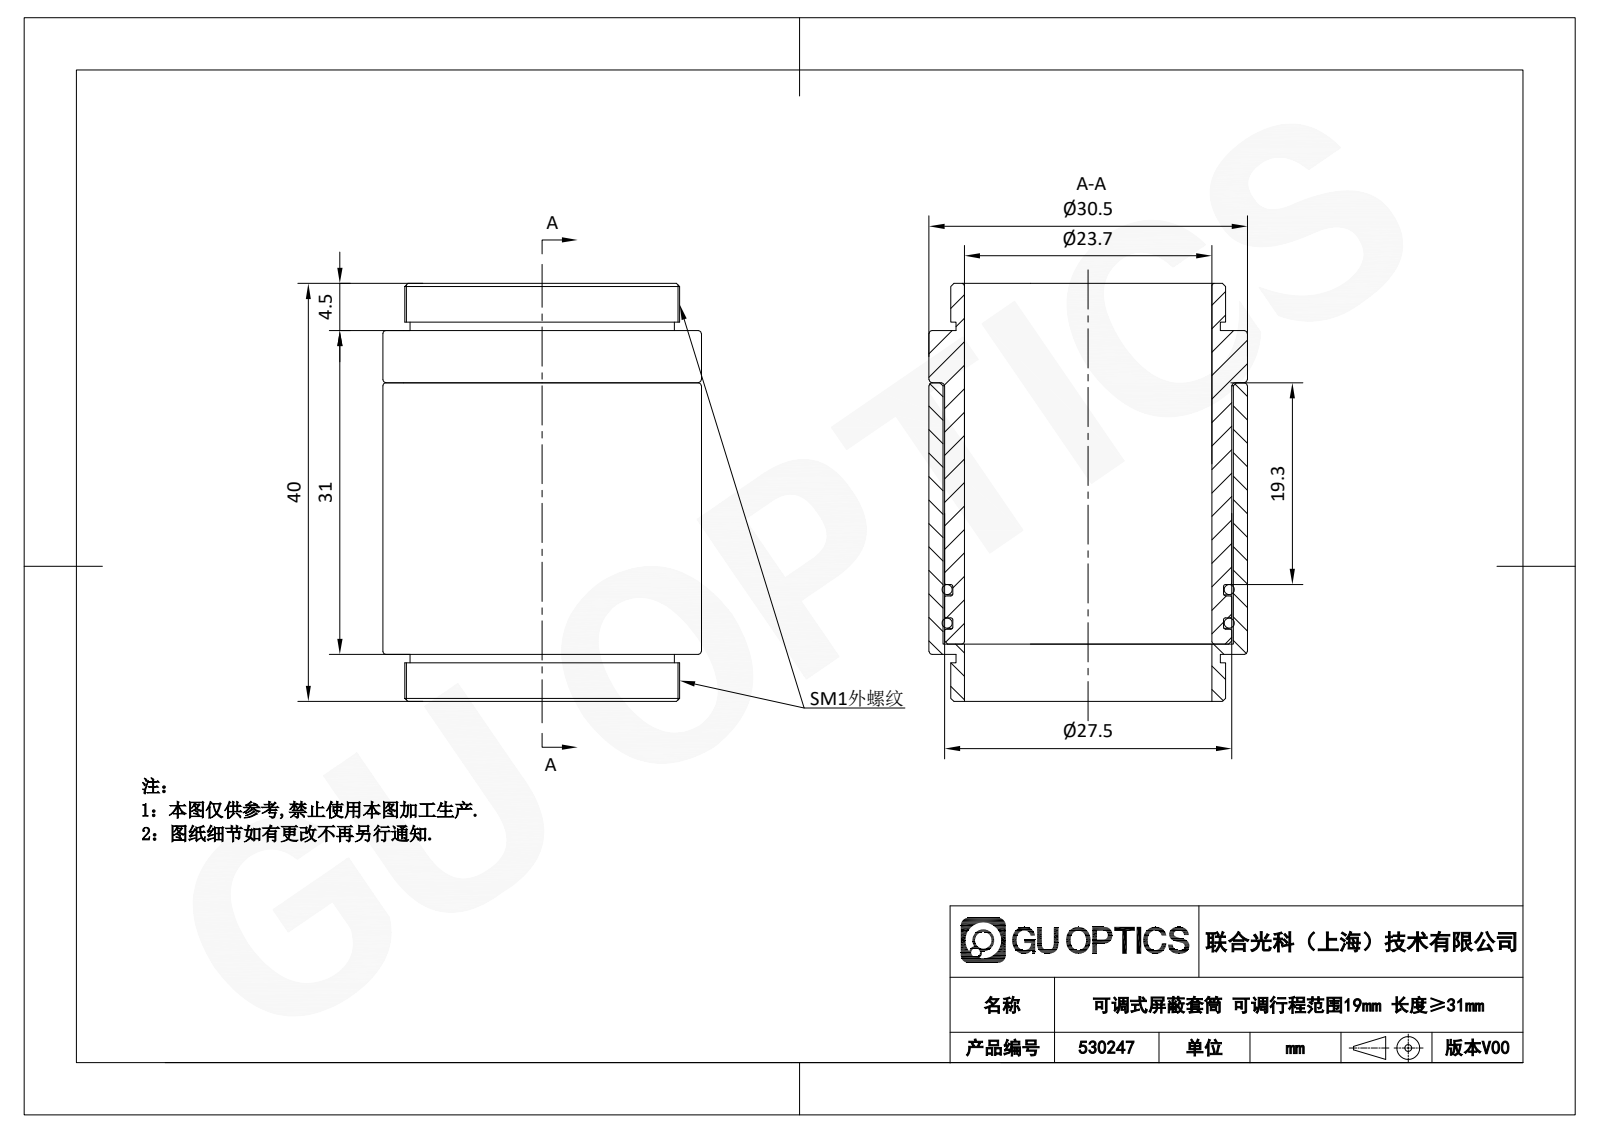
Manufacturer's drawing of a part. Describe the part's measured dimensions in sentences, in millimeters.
The part is named "3.03.31.15.207_SM1屏蔽套筒组件2_SM1-SC31-2_ZA; 24-26_O形圈; 530247; 3.03.31.15.206_SM1屏蔽套筒组件1_SM1-SC31-1_ZA". Its 3-D file was written by "SolidWorks 2020 (CONFIG_CONTROL_DESIGN)". It is 4 solids with 49 faces: 14 planar, 14 cylindrical and 21 other. Overall it measures 40 by 30.5 by 30.5 millimeters. Its volume is 9 462 cubic millimeters and its surface area 12 962 square millimeters. Round holes: 1 of diameter 23.7, 1 of diameter 27.8. Round bosses or shafts: 1 of diameter 30.5, 1 of diameter 27.5, 1 of diameter 26.3, 1 of diameter 25.9, 1 of diameter 25.3. The main face-to-face distances are 1, 30, 31, 5, 25, 26, 4.5, 35.5, 3.2, 1.1.
